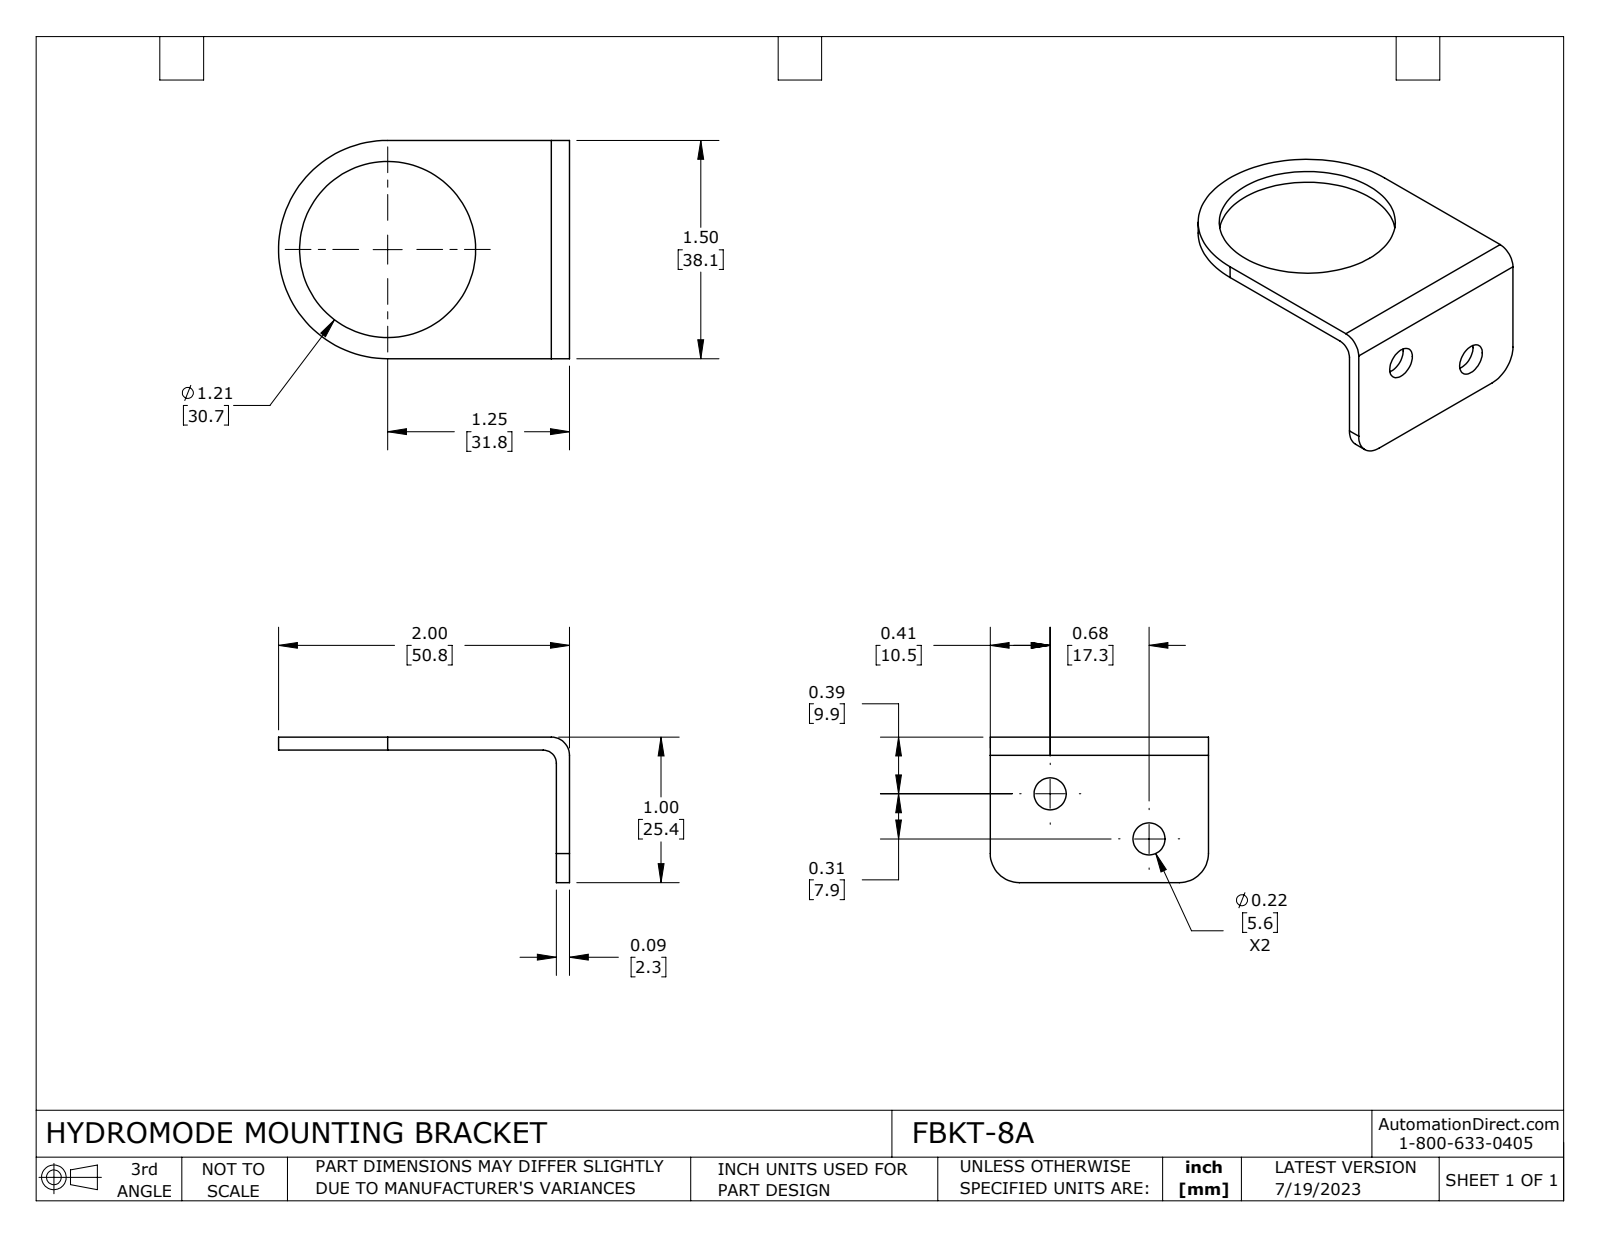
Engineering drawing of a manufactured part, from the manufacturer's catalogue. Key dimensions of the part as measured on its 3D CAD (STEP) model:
Part name (STEP PRODUCT): FBKT-8A
STEP written by: SolidWorks 2021 (CONFIG_CONTROL_DESIGN)
Units: inches
Bodies: 1 solid, 18 faces (7 planar, 11 cylindrical, 0 other)
Overall size (bounding box): 2 × 1.5 × 1
Volume: 0.257 in³ · Surface area: 6.806 in²
Round holes (diameter × count): ⌀0.22 ×2, ⌀1.21 ×1
Partial cylindrical surfaces — rounded edges, fillets, slot ends (radius × count): R0.2 ×2, R0.09 ×1, R0.125 ×1, R0.75 ×1
Main face-to-face distances: 0.09, 1.5, 0.91, 1
Hole centre spacings: 0.747
